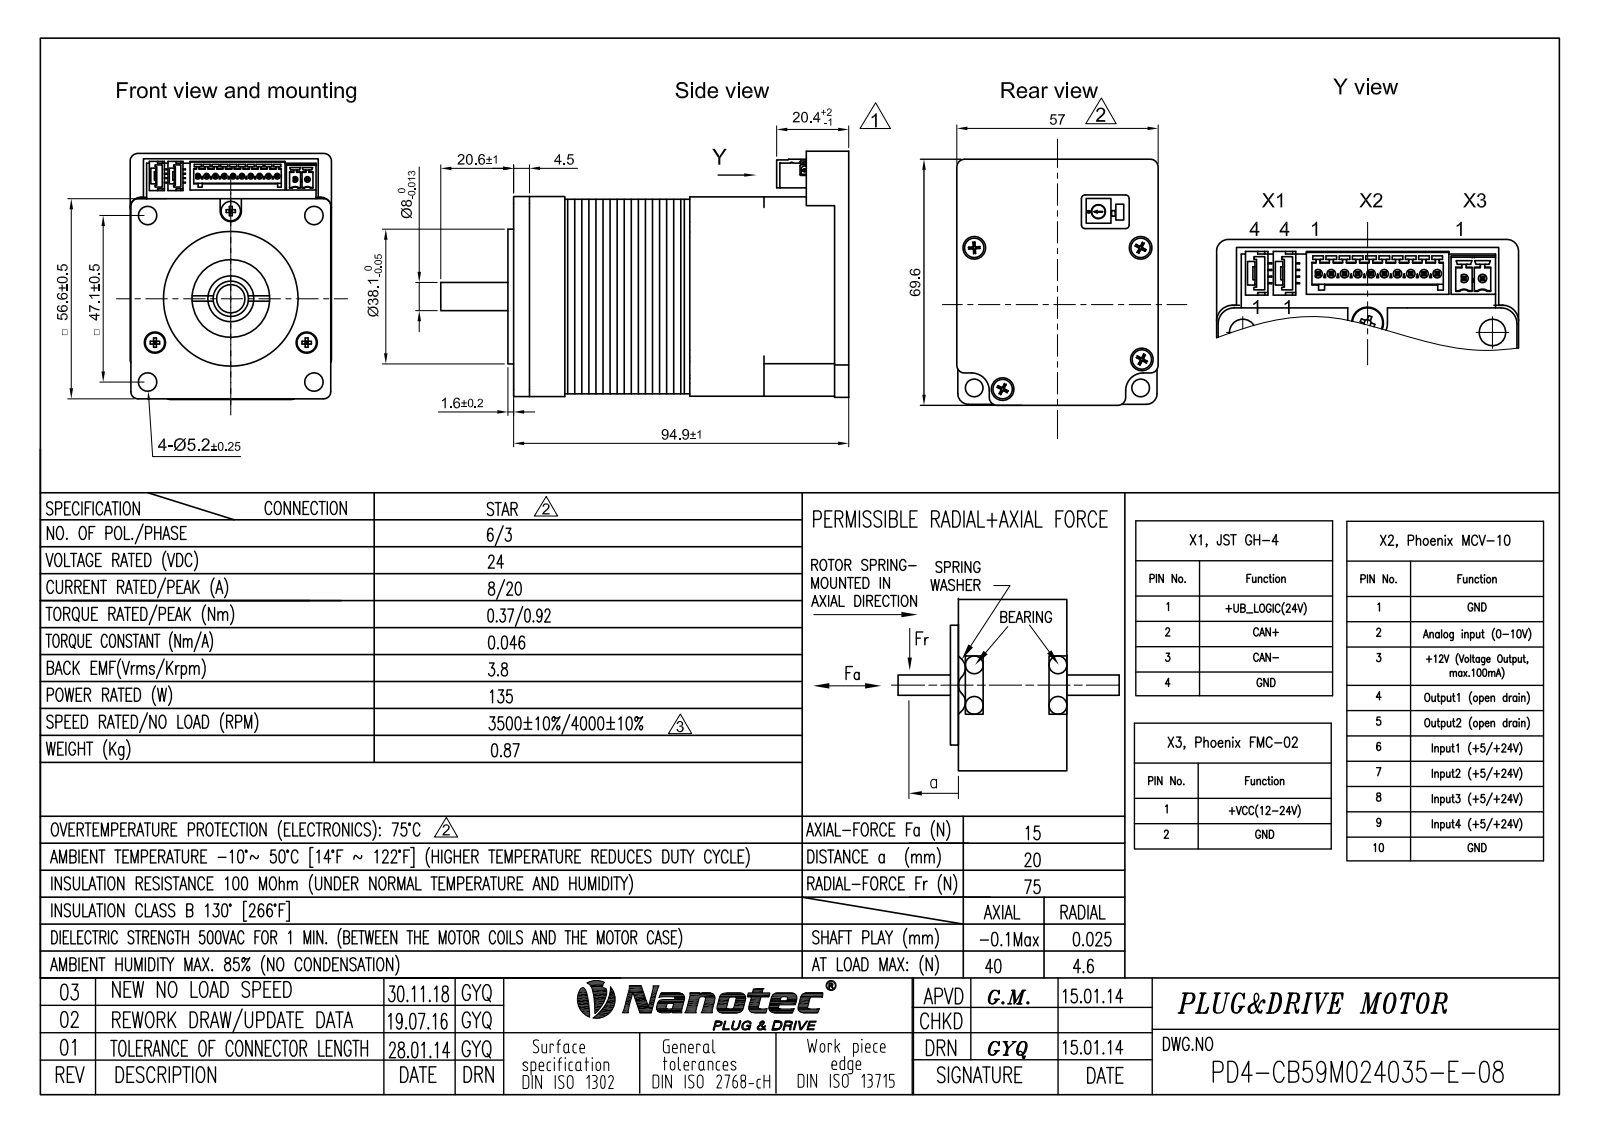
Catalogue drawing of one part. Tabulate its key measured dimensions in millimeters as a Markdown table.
| quantity | value |
| --- | --- |
| part name | 零件2 |
| STEP written by | Autodesk Inventor 2013 (AUTOMOTIVE_DESIGN) |
| units | millimeters |
| bodies | 0 solids, 1478 faces (1154 planar, 214 cylindrical, 110 other) |
| overall size | 115.5 × 69.6 × 57 |
| round holes (diameter × count) | 3 × 7, 3.4 × 4, 5.2 × 4, 2.5 × 3, 3.2 × 3, 2 × 2, 6 × 2, 3.78 × 1, 11 × 1, 13 × 1, 15 × 1, 22 × 1 |
| round bosses / shafts (diameter × count) | 1.2 × 12, 1.6 × 10, 5.5 × 7, 2.68 × 4, 12 × 3, 0.46 × 2, 56.6 × 1, 38.1 × 1 |
| partial cylindrical surfaces (radius × count) | 0.2 × 26, 0.16 × 20, 2 × 20, 1 × 14, 0.21 × 8, 2.2 × 6, 2.5 × 6, 3 × 5 |
| main face-to-face distances | 82.4, 19, 10.3, 5, 77.4, 7.9, 5.3, 72.1, 2.9, 2.4 |
| hole center spacings | 47.1, 27.41, 28.5, 33.3, 40.61, 24.8, 42.96, 7.5 |
